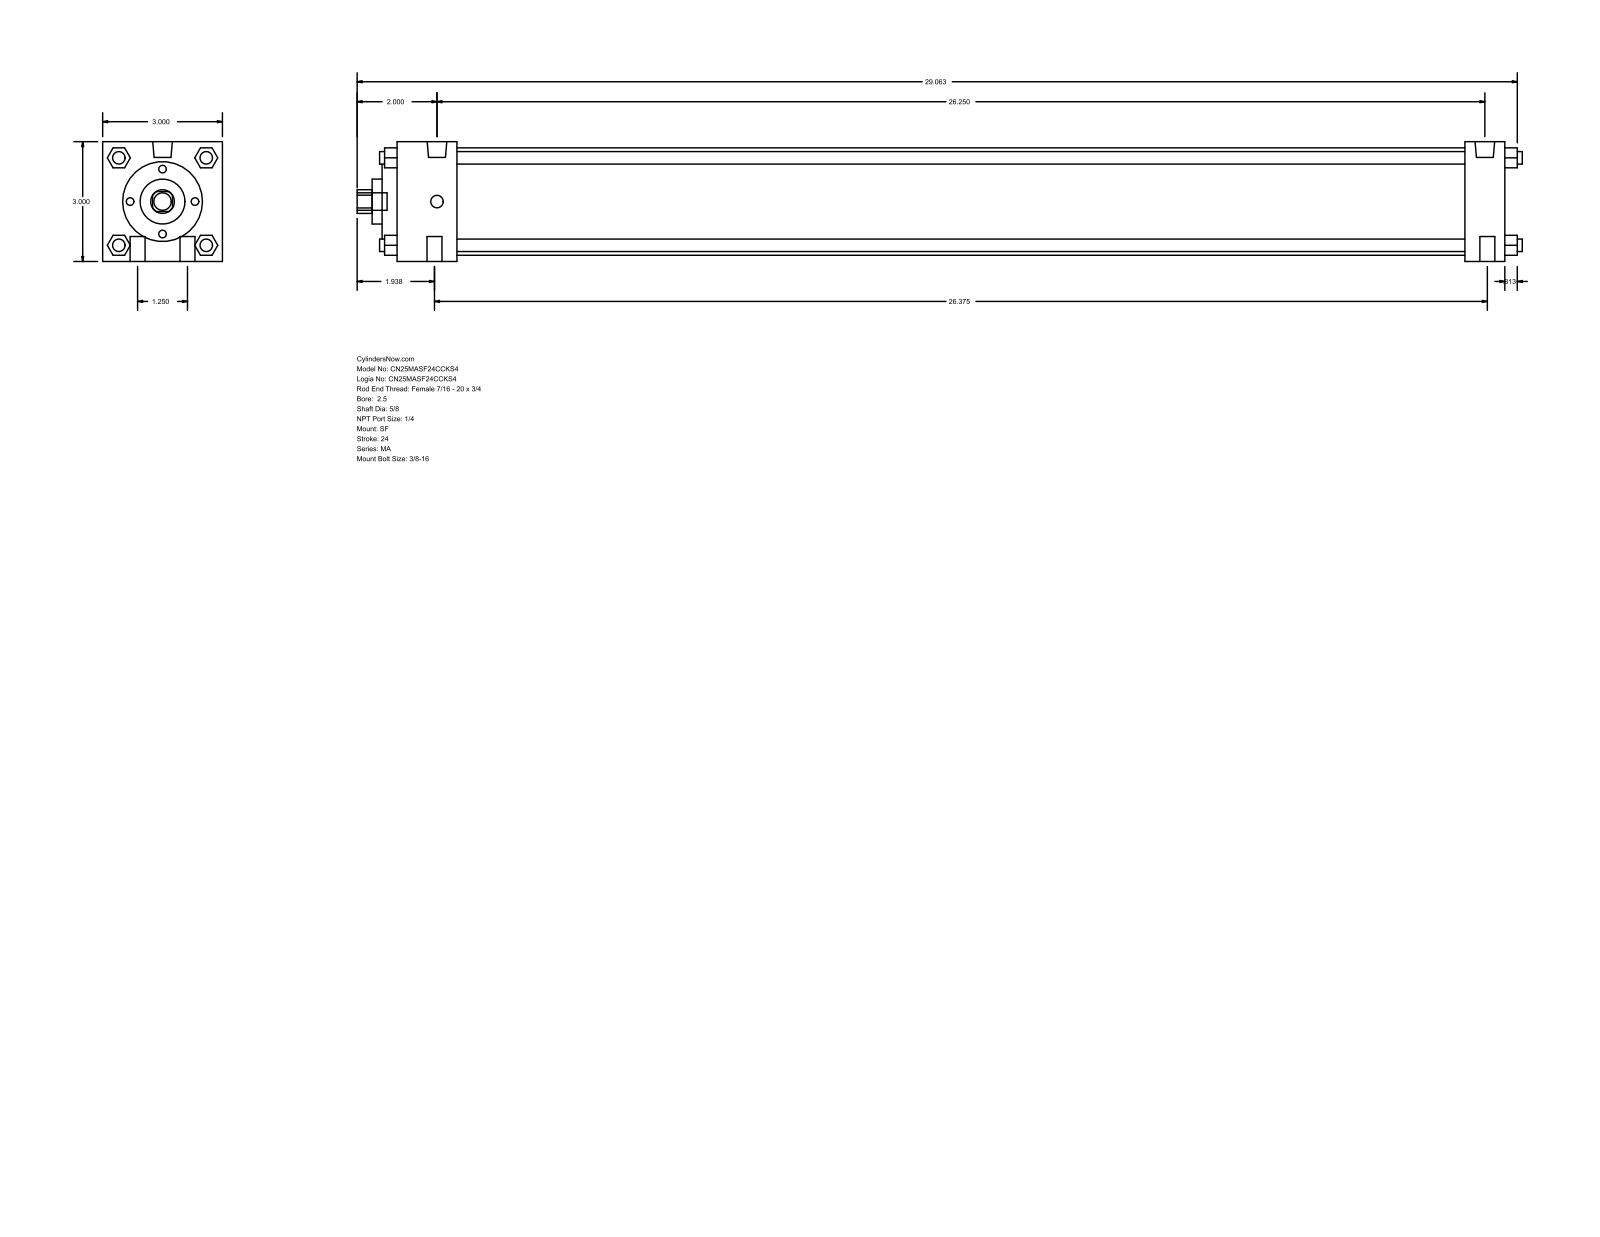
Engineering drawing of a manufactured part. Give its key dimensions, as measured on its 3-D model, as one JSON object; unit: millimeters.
{"part_name": "MA_SF__0250_0.625", "step_written_by": "GSSL Pune (CONFIG_CONTROL_DESIGN)", "units": "millimeters", "bodies": {"solids": 0, "faces": 126, "planar": 95, "cylindrical": 31, "other": 0}, "overall_size": [741.36, 76.2, 76.2], "round_holes": [[15.88, 1], [28.57, 1], [50.8, 1], [68.33, 1]], "round_bosses_or_shafts": [[7.94, 6], [9.53, 4], [12.49, 2], [11.11, 1]], "partial_cylinders_radius": [[7.54, 1]], "face_to_face_distances": [76.2, 704.85, 25.4, 679.45, 38.1, 641.35, 666.75, 12.7, 9.52, 47.62]}
